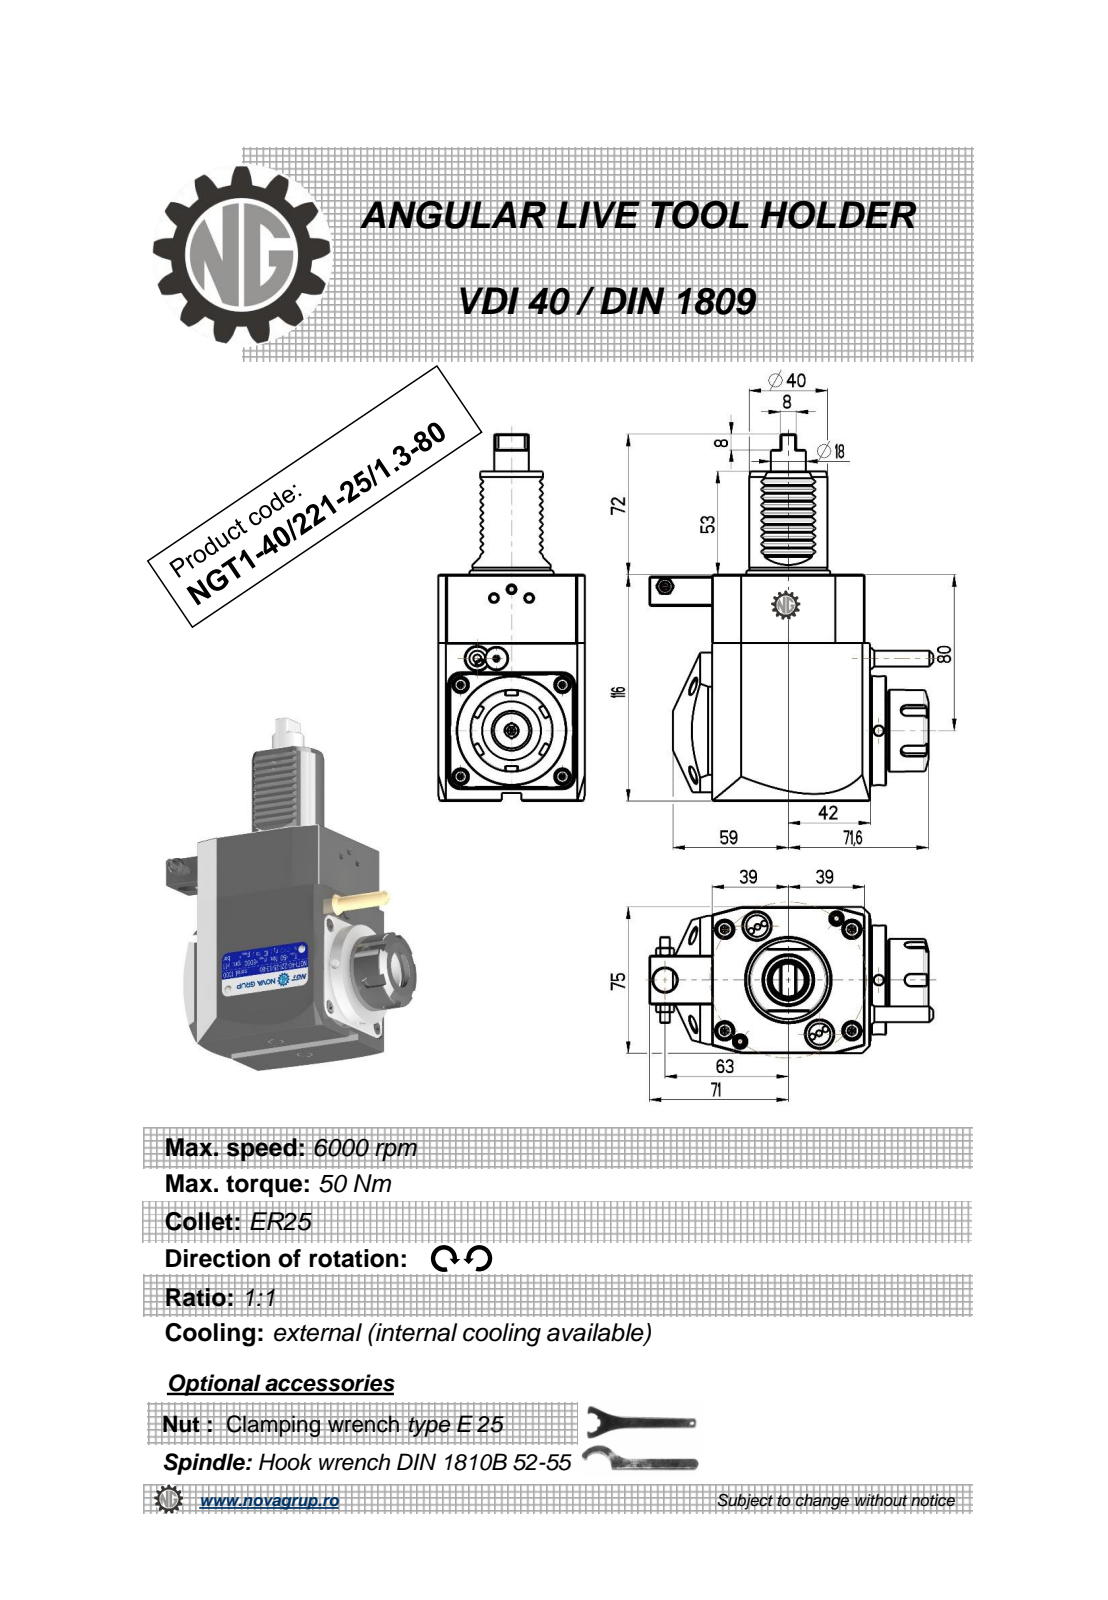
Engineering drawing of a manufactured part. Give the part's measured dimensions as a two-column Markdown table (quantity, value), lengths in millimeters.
| quantity | value |
| --- | --- |
| part name | NGT1_40_221_25_1_3_80 |
| STEP written by | PRO/ENGINEER BY PARAMETRIC TECHNOLOGY CORPORATION, 2010280 (CONFIG_CONTROL_DESIGN) |
| units | millimeters |
| bodies | 1 solid, 471 faces (228 planar, 94 cylindrical, 149 other) |
| overall size | 188 × 145.14 × 75 |
| volume | 854 915 mm³ |
| surface area | 70 111 mm² |
| round holes (diameter × count) | 5 × 3, 3 × 1, 4.2 × 1, 9.5 × 1, 12 × 1, 20.3 × 1 |
| round bosses / shafts (diameter × count) | 56 × 1, 43 × 1, 42 × 1, 40 × 1, 33 × 1, 17.8 × 1, 11.2 × 1, 8.96 × 1 |
| partial cylindrical surfaces (radius × count) | 0.3 × 20, 0.26 × 12, 0.22 × 6, 3 × 5, 0.8 × 2, 40 × 1 |
| main face-to-face distances | 75, 116, 81, 78, 3, 11, 8, 80.8, 2.8, 89 |
| hole center spacings | 39.58, 40.93, 72.5, 109.25, 131.95 |
